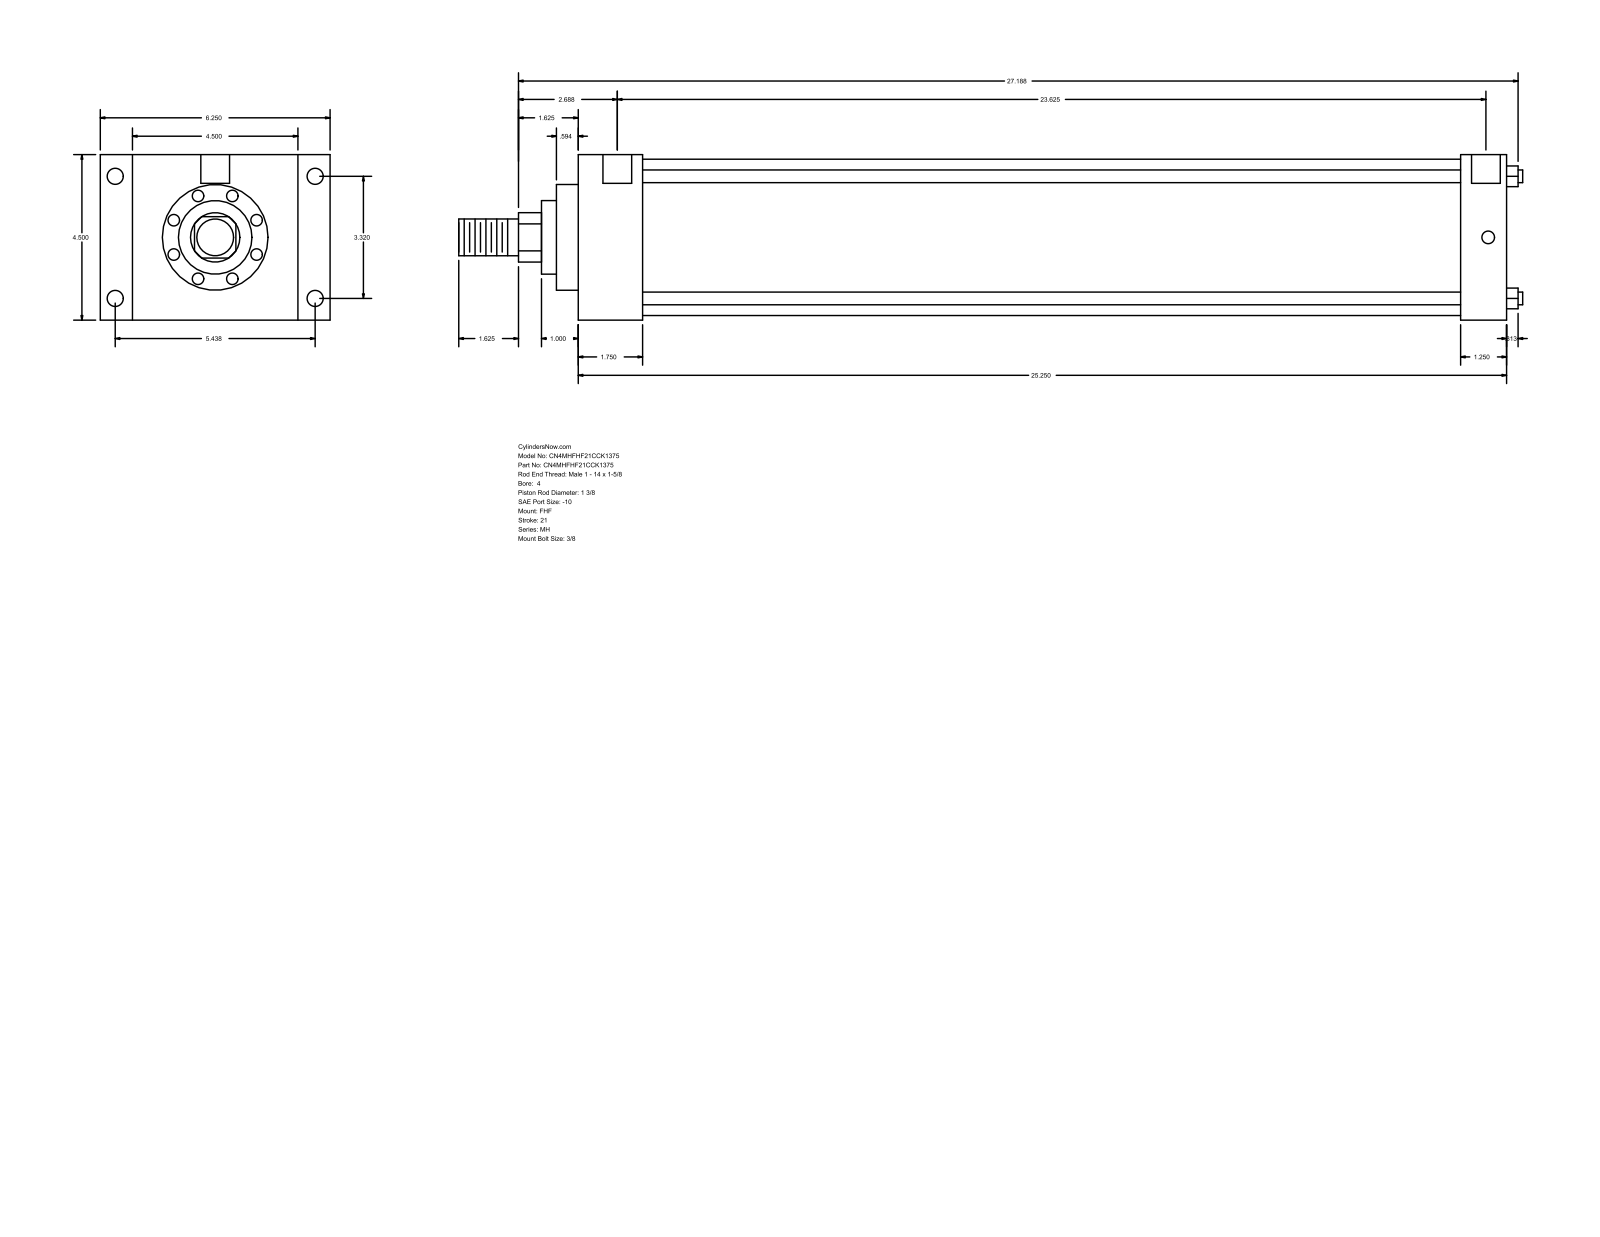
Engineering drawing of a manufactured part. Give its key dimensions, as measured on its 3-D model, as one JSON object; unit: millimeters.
{"part_name": "MH_FHF__0400_1.375", "step_written_by": "GSSL Pune (CONFIG_CONTROL_DESIGN)", "units": "millimeters", "bodies": {"solids": 0, "faces": 90, "planar": 61, "cylindrical": 29, "other": 0}, "overall_size": [735.01, 158.75, 114.3], "round_holes": [[8.73, 4], [11.13, 4], [19.84, 2]], "round_bosses_or_shafts": [[8.76, 4], [107.95, 1], [73.03, 1], [50.8, 1], [34.92, 1], [25.4, 1]], "partial_cylinders_radius": [[17.06, 1]], "face_to_face_distances": [114.3, 641.35, 44.45, 596.9, 22.23, 136.53, 158.76, 609.61, 565.16, 31.74], "hole_center_spacings": [84.32, 138.12, 161.82, 603.25, 1.58, 1.59, 600.08, 601.66]}
